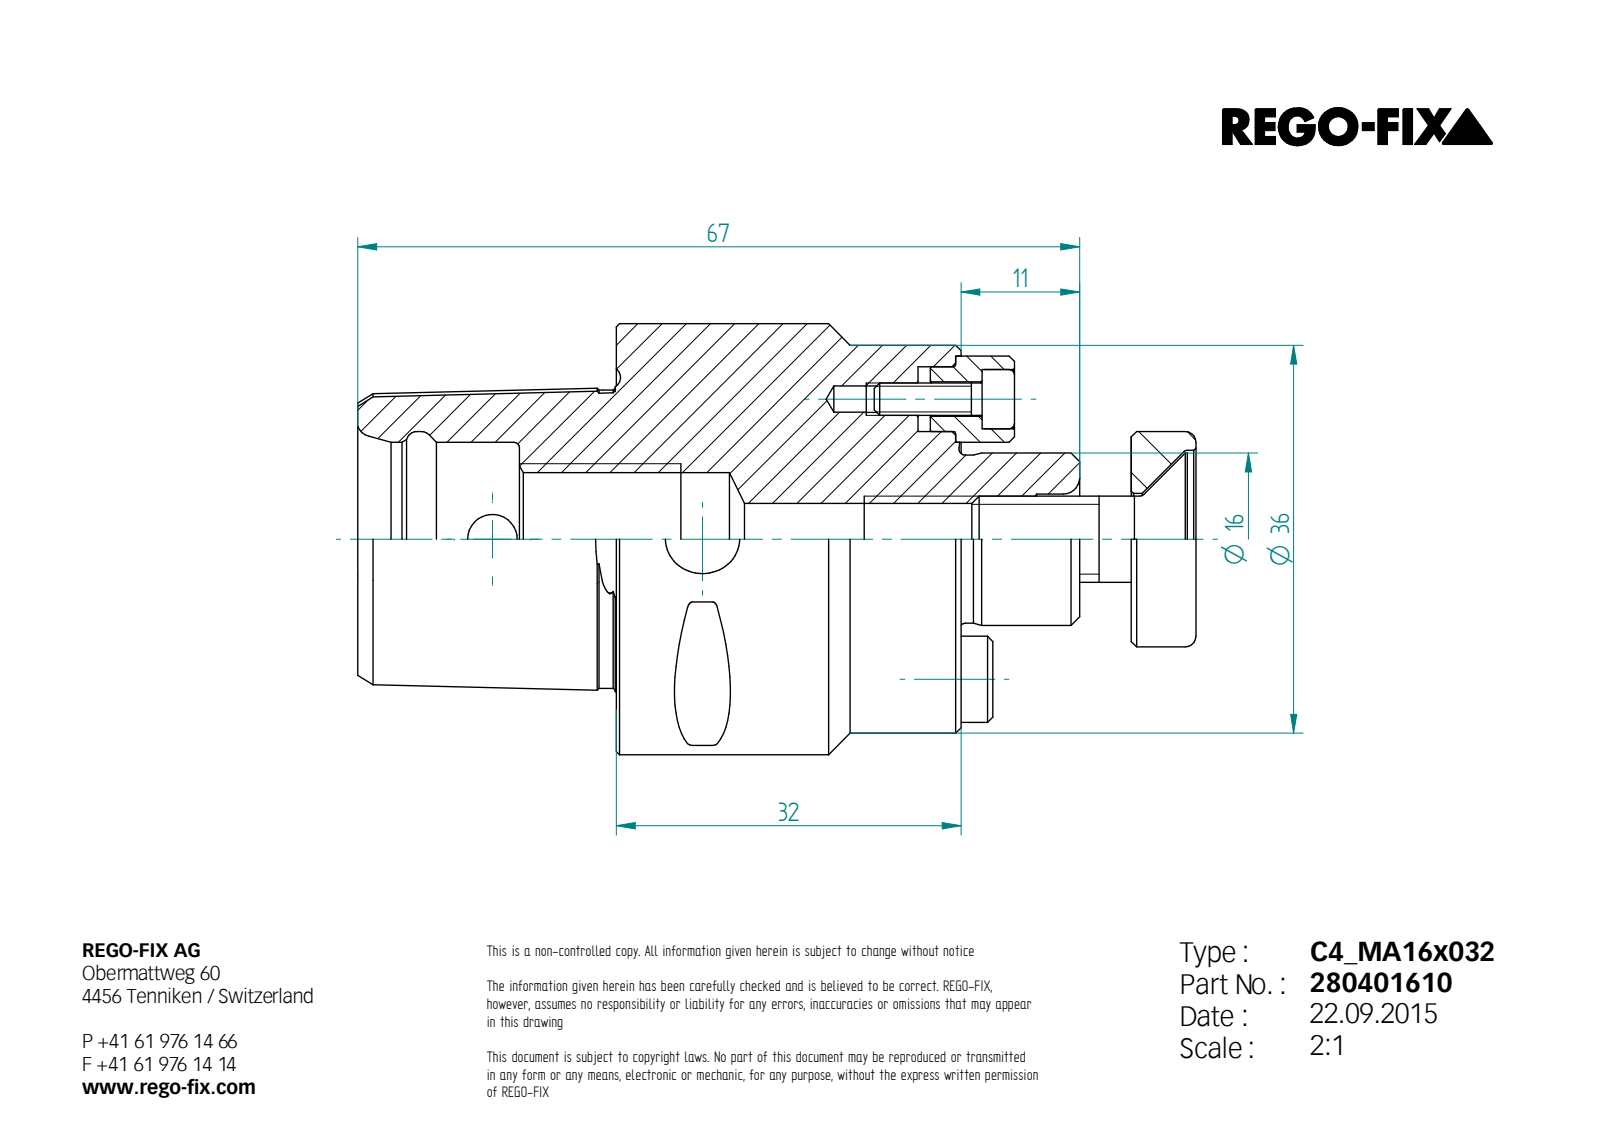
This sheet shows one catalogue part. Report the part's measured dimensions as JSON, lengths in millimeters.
{"part_name": "0003464; 0003381; 0007093; 0004885 (+1 more)", "step_written_by": "Unknown (AUTOMOTIVE_DESIGN)", "units": "millimeters", "bodies": {"solids": 7, "faces": 205, "planar": 51, "cylindrical": 52, "other": 102}, "overall_size": [77.8, 40, 40], "volume_mm3": 47957, "surface_area_mm2": 14394, "round_holes": [[2.44, 2], [2.46, 2], [3.2, 2], [5.5, 2], [6, 2], [8, 2], [4, 1], [4.6, 1], [6.65, 1], [8.4, 1], [8.5, 1], [12.38, 1]], "round_bosses_or_shafts": [[3, 2], [40, 1], [36, 1], [16, 1], [15.6, 1], [8, 1]], "partial_cylinders_radius": [[0.5, 8], [3, 1]], "face_to_face_distances": [32, 47.8, 15.8, 53, 21, 5.2, 24, 56, 71.8, 77], "hole_center_spacings": [13, 23.5, 26]}
